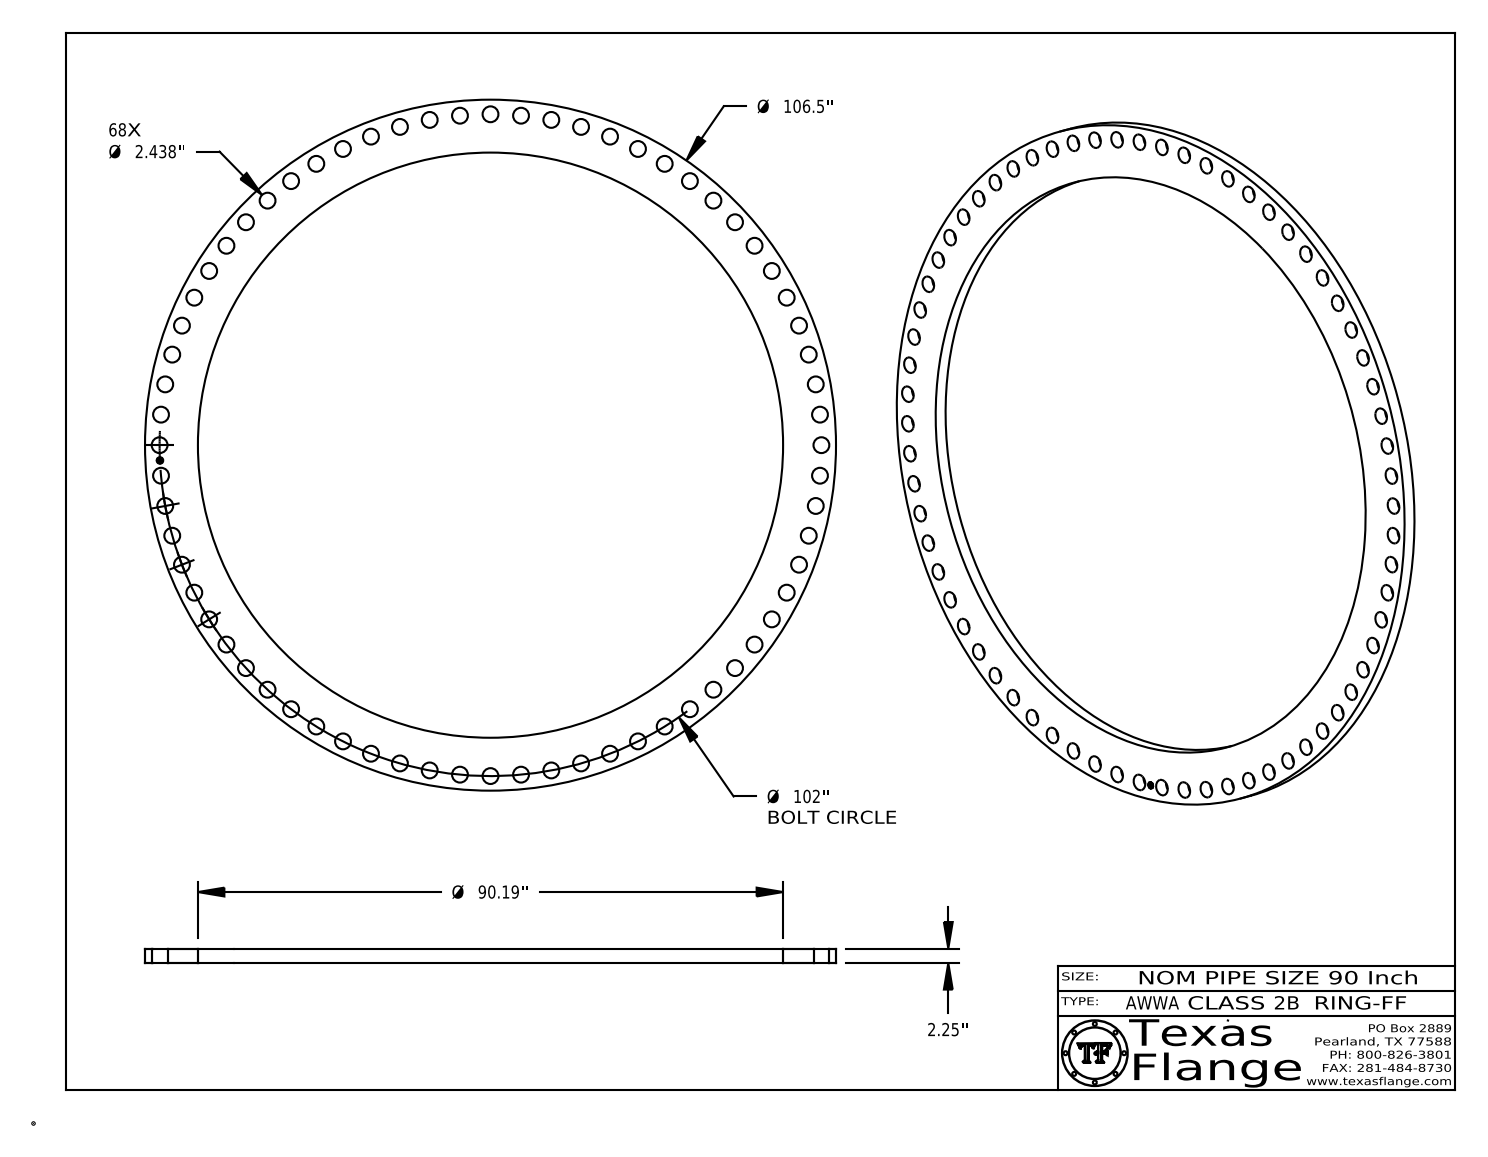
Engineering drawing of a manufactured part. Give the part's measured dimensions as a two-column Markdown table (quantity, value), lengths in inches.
| quantity | value |
| --- | --- |
| part name | AWWA Class 2B-RING-FF |
| STEP written by | CATIA V5 STEP AP214 (AUTOMOTIVE_DESIGN) |
| units | inches |
| bodies | 1 solid, 527 faces (367 planar, 160 cylindrical, 0 other) |
| overall size | 106.5 × 106.5 × 2.25 |
| volume | 4 955 in³ |
| surface area | 6 967 in² |
| round holes (diameter × count) | 2.438 × 68, 1 × 1, 90.19 × 1 |
| round bosses / shafts (diameter × count) | 0.061 × 8, 106.5 × 1, 0.788 × 1 |
| main face-to-face distances | 2.25, 0.015, 2.235, 0.019, 0.298, 0.292, 0.054, 0.194, 0.248, 0.044 |
| hole center spacings | 51, 9.411, 18.743, 4.711, 23.353, 14.092, 32.415, 41.2 |
